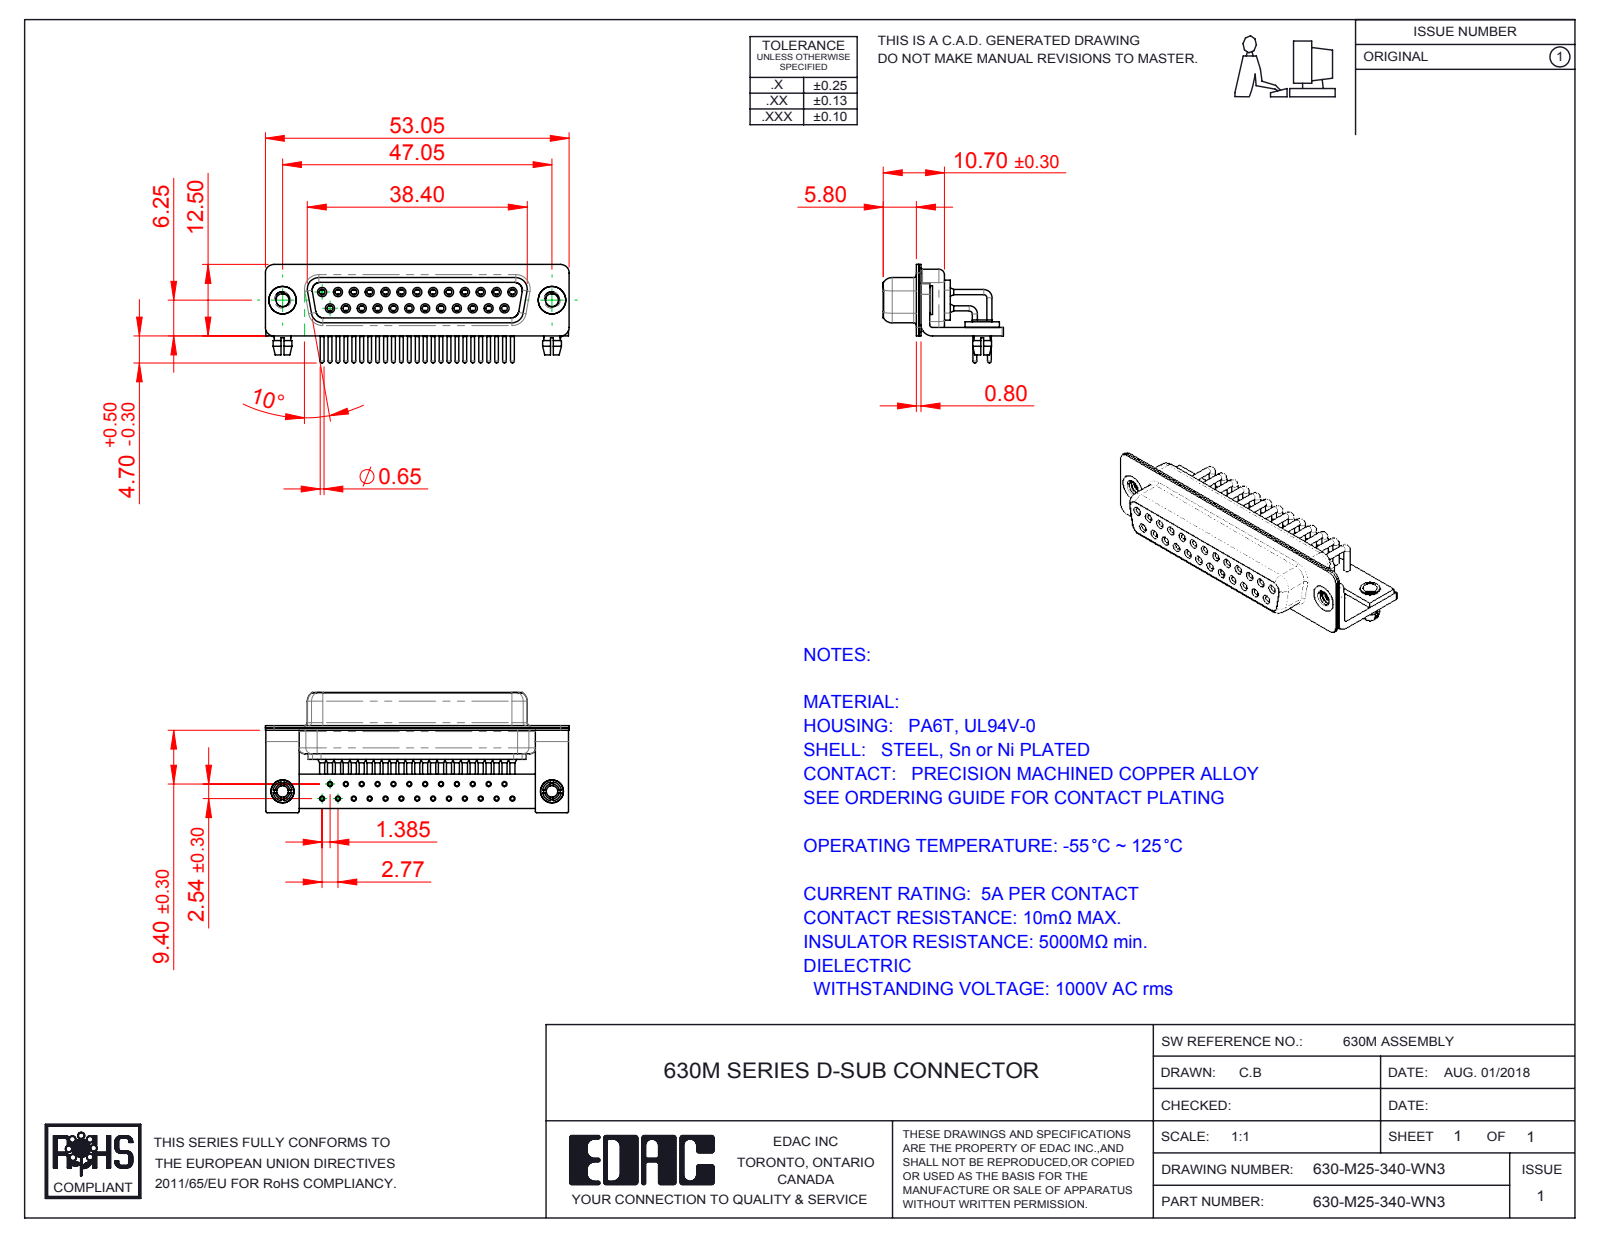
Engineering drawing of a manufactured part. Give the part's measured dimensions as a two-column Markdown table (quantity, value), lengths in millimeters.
| quantity | value |
| --- | --- |
| part name | 630M Shell Rear_25 Contacts; 630M 4-40 Threaded Rivet_Stabilizer; 630M Housing_25 Contacts; 630M Shell Front_25 Contacts (+6 more) |
| STEP written by | SolidWorks 2016 (CONFIG_CONTROL_DESIGN) |
| units | millimeters |
| bodies | 35 solids, 1796 faces (516 planar, 816 cylindrical, 464 other) |
| overall size | 53.05 × 21 × 17.2 |
| volume | 4 497 mm³ |
| surface area | 11 342 mm² |
| round holes (diameter × count) | 2 × 27, 0.9 × 25, 1 × 25, 1.1 × 25, 1.7 × 25, 1.8 × 25, 2.26 × 2, 2.5 × 2, 3.2 × 2, 4 × 2, 4.8 × 2 |
| round bosses / shafts (diameter × count) | 1.6 × 25, 1.5 × 25, 0.9 × 25, 0.65 × 25, 5 × 2, 4.9 × 2, 4 × 2, 3.4 × 2 |
| partial cylindrical surfaces (radius × count) | 0.25 × 16, 1.5 × 16, 2 × 13, 1.35 × 10, 1.6 × 8, 0.5 × 5, 0.6 × 4, 0.65 × 4 |
| main face-to-face distances | 0.4, 2.3, 1.9, 9.35, 1.45, 8.95, 0.85, 0.8, 6.2, 1 |
| hole center spacings | 2.77, 5.54, 8.31, 11.08, 13.85, 3.16, 4.87, 16.62 |
